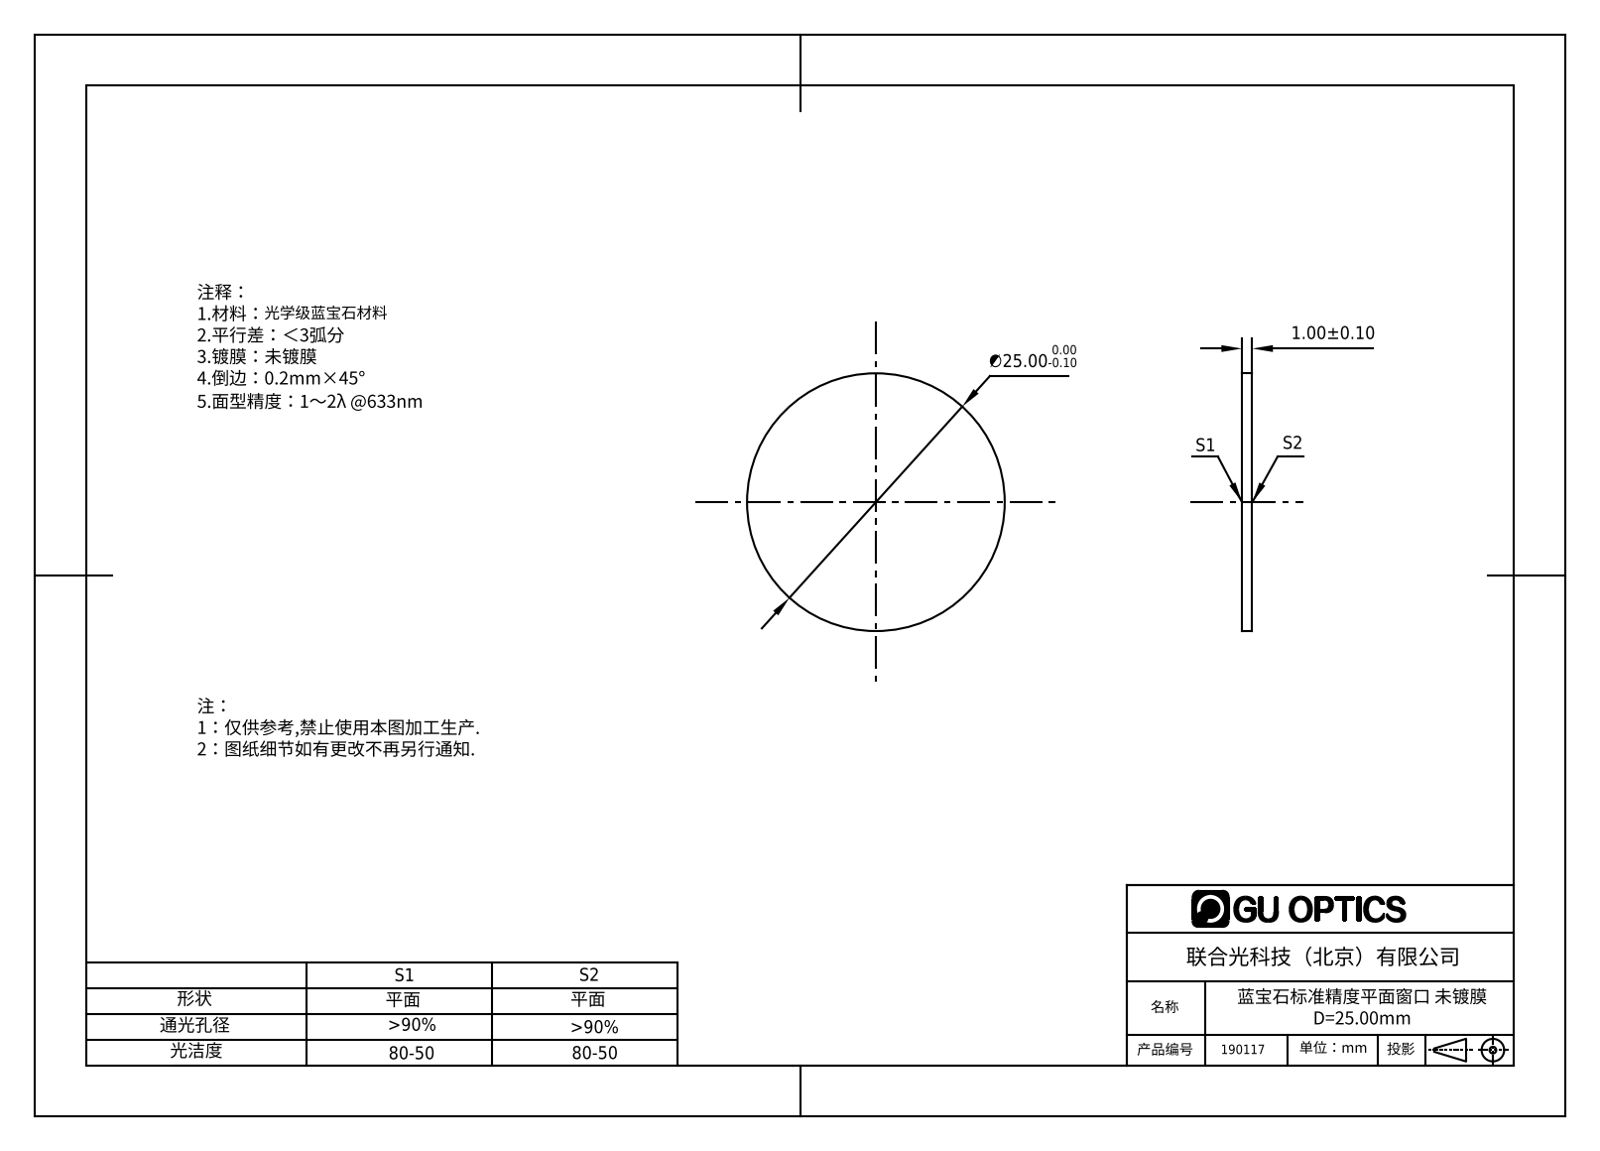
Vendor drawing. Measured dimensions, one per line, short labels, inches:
name: 190117
written by: SolidWorks 2016 (AUTOMOTIVE_DESIGN)
unit: in
bodies: 1 solid, 4 faces (2 planar, 2 cylindrical, 0 other)
size: 0.984 × 0.984 × 0.039
volume: 0.03 in³; area: 1.643 in²
bosses: 1× ⌀0.984
face distances: 0.039
